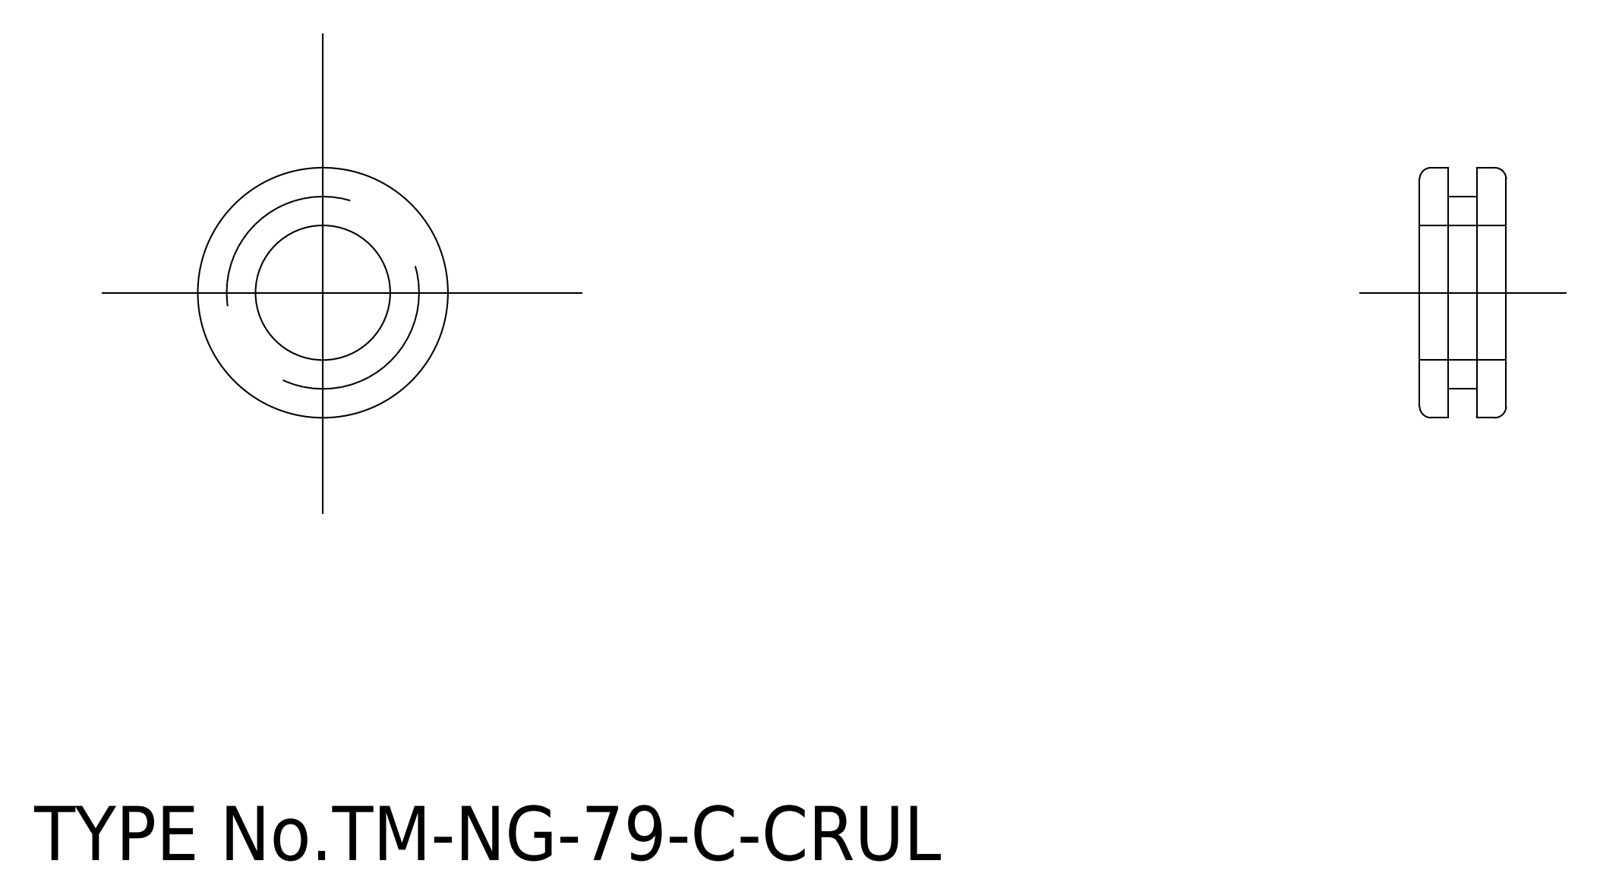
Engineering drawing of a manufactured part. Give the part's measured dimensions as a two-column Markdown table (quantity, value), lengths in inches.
| quantity | value |
| --- | --- |
| STEP written by | spGate 15.6.1 (AUTOMOTIVE_DESIGN) |
| units | inches |
| bodies | 1 solid, 16 faces (4 planar, 8 cylindrical, 4 other) |
| overall size | 0.512 × 0.512 × 0.177 |
| volume | 0.021 in³ |
| surface area | 0.843 in² |
| round holes (diameter × count) | 0.276 × 1 |
| round bosses / shafts (diameter × count) | 0.512 × 1, 0.394 × 1 |
| main face-to-face distances | 0.059, 0.118, 0.177 |
